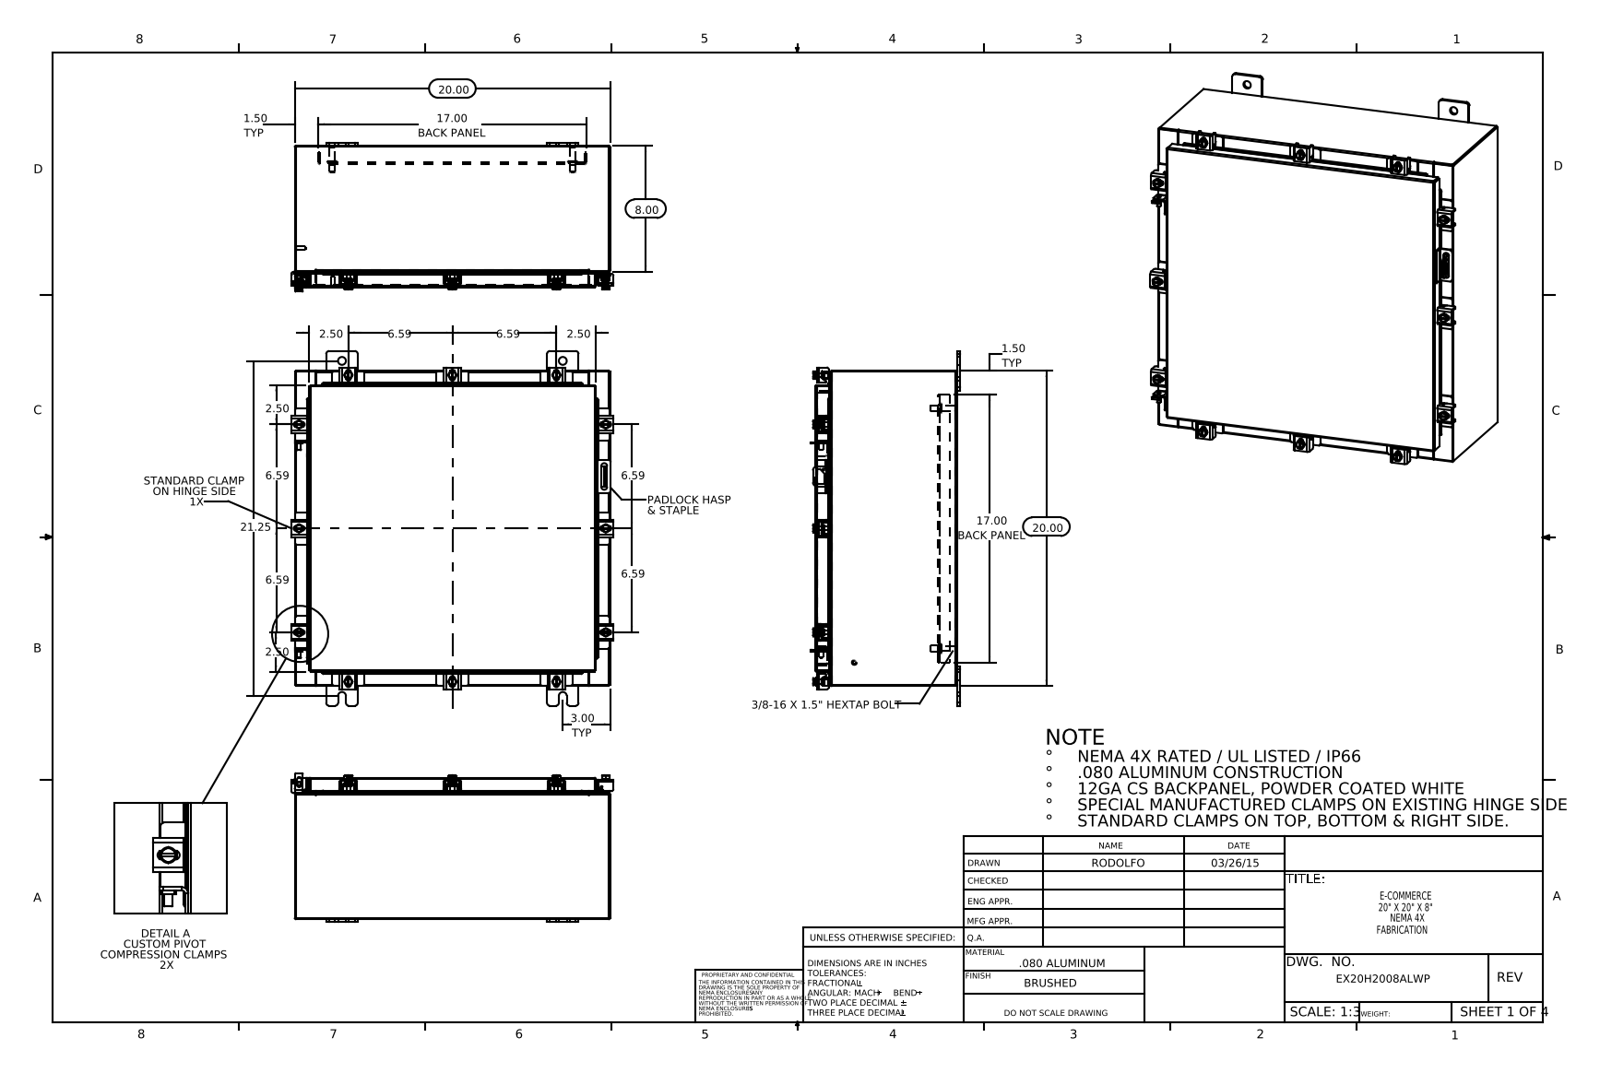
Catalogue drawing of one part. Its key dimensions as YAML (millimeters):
part_name: "EX20H2008ALWP Bottom; EX20H2008ALWP Padlock Hasp; N-WMT04X30402202210-00 Clamp Top; Quarter-20 CD Stud (+8 more)"
step_written_by: "SolidWorks 2014 (CONFIG_CONTROL_DESIGN)"
units: millimeters
bodies: {solids: 81, faces: 2018, planar: 1075, cylindrical: 783, other: 160}
overall_size: [571.5, 518.7, 240.1]
volume: 2648000
surface_area: 2615000
round_holes:
  - {diameter: 5.4, count: 12}
  - {diameter: 6.6, count: 12}
  - {diameter: 12.7, count: 8}
  - {diameter: 3.2, count: 1}
  - {diameter: 6.4, count: 1}
round_bosses_or_shafts:
  - {diameter: 12.7, count: 12}
  - {diameter: 6.4, count: 12}
  - {diameter: 10.1, count: 10}
  - {diameter: 15.9, count: 4}
  - {diameter: 9.5, count: 4}
  - {diameter: 8.4, count: 4}
  - {diameter: 8, count: 2}
  - {diameter: 6, count: 2}
partial_cylinders:
  - {radius: 1.5, count: 54}
  - {radius: 0.3, count: 24}
  - {radius: 3.6, count: 24}
  - {radius: 4.8, count: 24}
  - {radius: 2.2, count: 22}
  - {radius: 3, count: 22}
  - {radius: 2.3, count: 18}
  - {radius: 1.3, count: 17}
face_to_face_distances: [1.9, 226.1, 506.1, 228, 224.2, 504.2, 508, 2.6, 25.4, 27.3]
hole_center_spacings: [167.5, 259.5, 422.1, 482.5, 521.7, 59.4, 365.1, 441.5]
